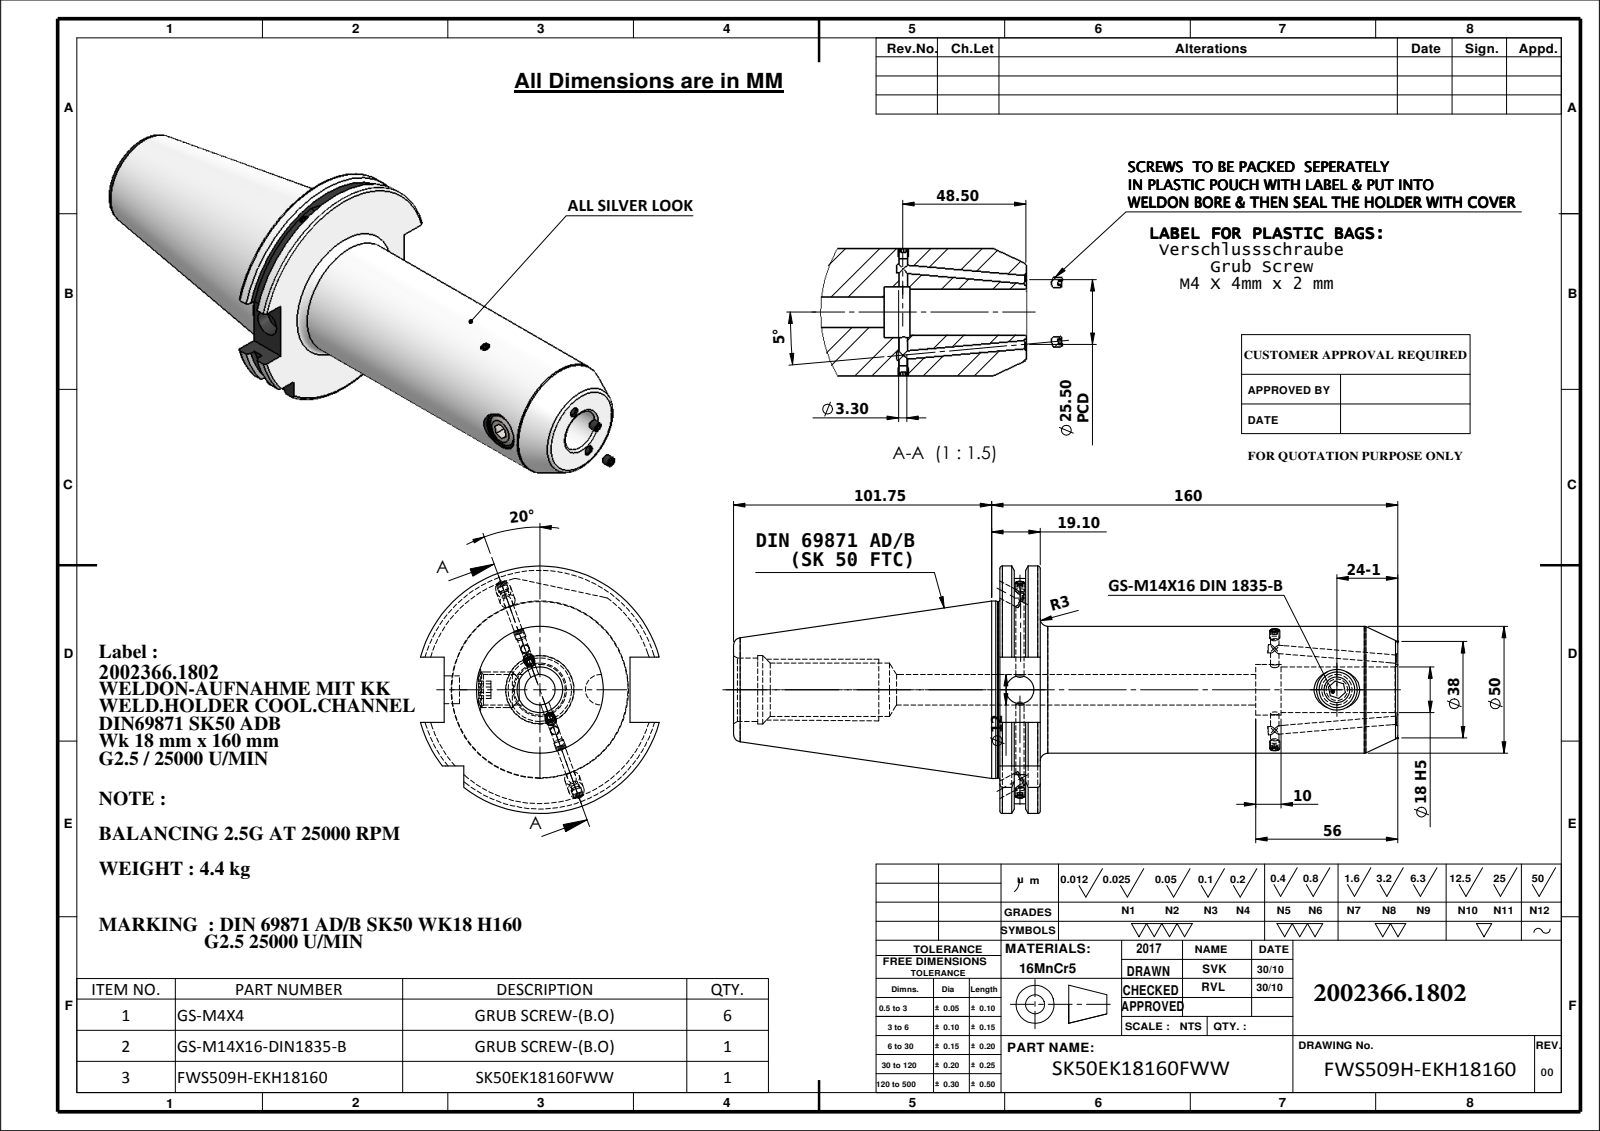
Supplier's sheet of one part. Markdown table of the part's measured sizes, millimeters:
| quantity | value |
| --- | --- |
| part name | Copy of M4X4_DIN 913 - M4 x 4-N; M14X16_ISO 4026 - M12 x 12-N; 91506-WK218160; SK50EK18160FWW |
| STEP written by | SolidWorks 2009 (CONFIG_CONTROL_DESIGN) |
| units | millimeters |
| bodies | 8 solids, 252 faces (93 planar, 83 cylindrical, 76 other) |
| overall size | 275.84 × 97.5 × 94.05 |
| volume | 576 845 mm³ |
| surface area | 74 404 mm² |
| round holes (diameter × count) | 3.3 × 4, 4.2 × 2, 6 × 2, 12 × 2, 11 × 1, 16 × 1, 18 × 1, 20 × 1, 21 × 1, 25 × 1, 27 × 1 |
| round bosses / shafts (diameter × count) | 4 × 6, 69.85 × 1, 69.45 × 1, 50 × 1, 14 × 1 |
| partial cylindrical surfaces (radius × count) | 44.9 × 1, 48.75 × 1 |
| main face-to-face distances | 15.9, 156.8, 140.9, 5.66, 10.24, 151.14, 10.15, 4.49, 5.75, 146.65 |
| hole center spacings | 100.4, 124.9 |
